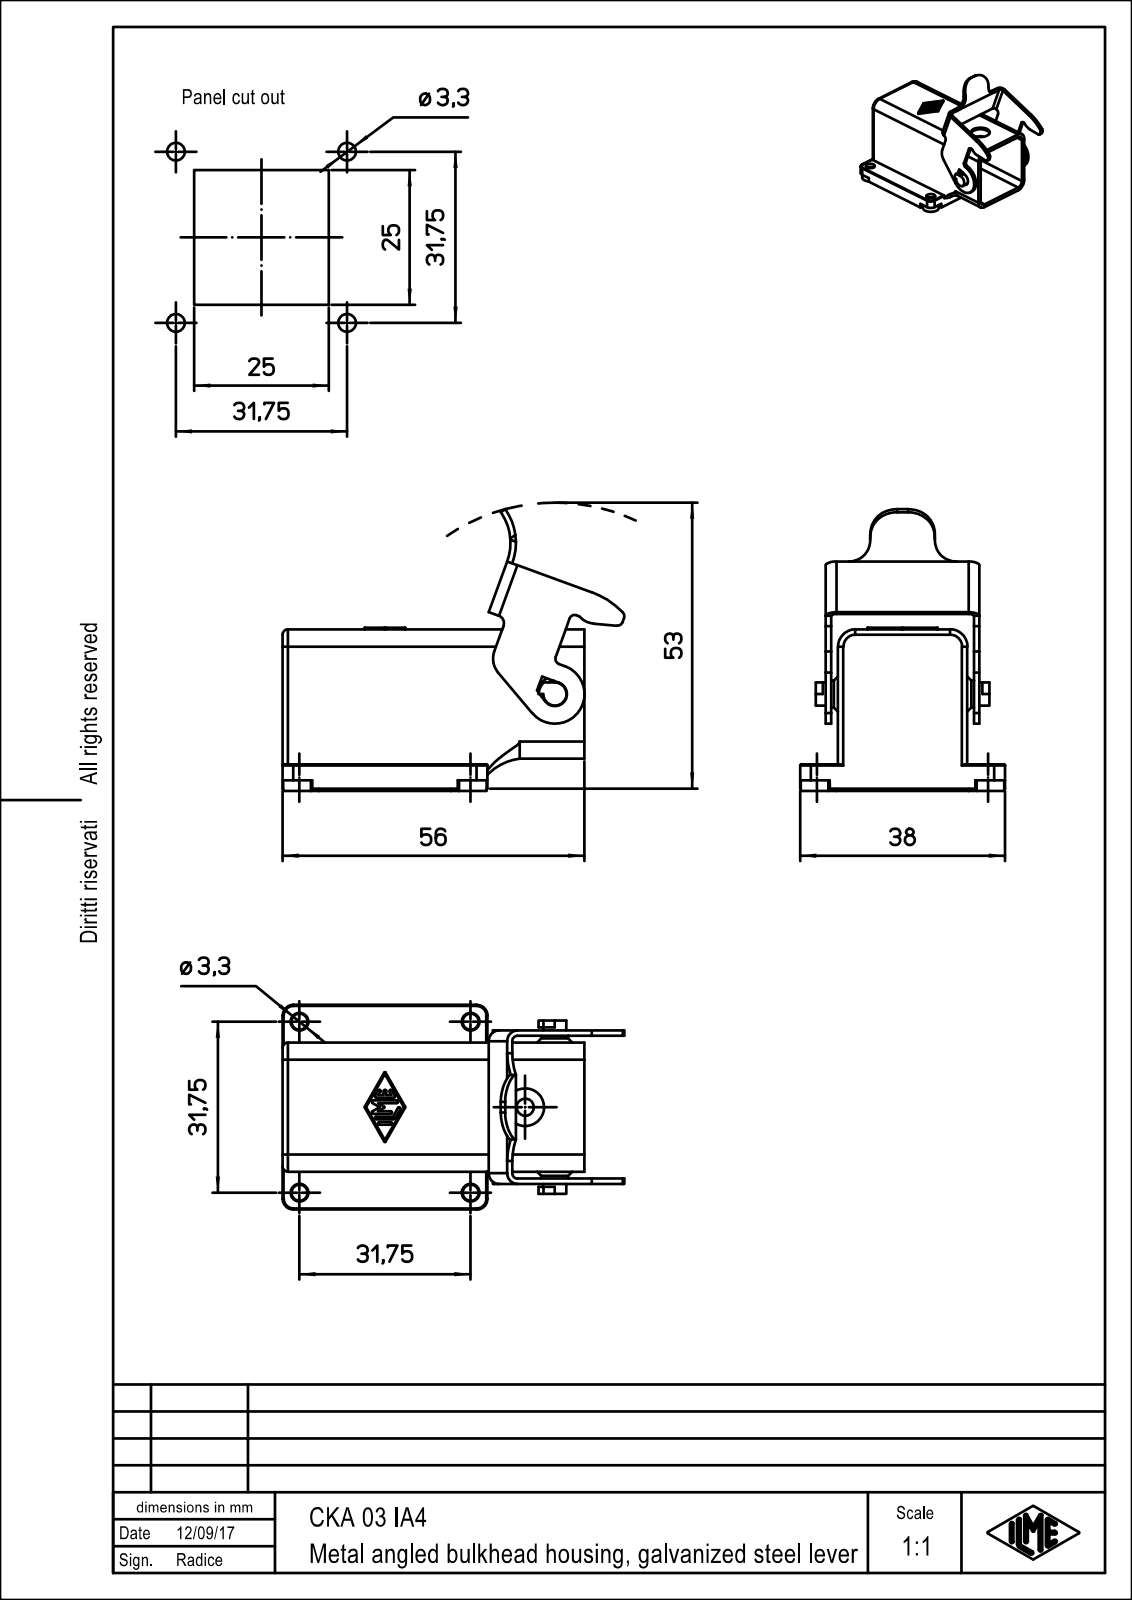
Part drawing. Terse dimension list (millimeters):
name: CKA_03_IA4
written by: PTC Creo Elements/Direct Modeling 19.0E 27-Jun-2016 (C) Parametric Technology GmbH (AUTOMOTIVE_DESIGN)
unit: mm
bodies: 1 solid, 310 faces (159 planar, 127 cylindrical, 24 other)
size: 63.4 × 52.31 × 38
volume: 14 191 mm³; area: 15 190 mm²
holes: 4× ⌀3, 4× ⌀3.3, 1× ⌀3.2, 1× ⌀7
bosses: 1× ⌀5, 1× ⌀4.3
rounds: 21× R2, 15× R0.25, 12× R3.2, 9× R1, 5× R3, 4× R0.2, 4× R0.5, 4× R4
face distances: 1.2, 22.8, 24, 25.05, 21.6, 1, 2.25, 27.5, 3.45, 26.25
hole spacings: 31.76, 18.84, 31.75, 44.79, 44.91, 31.74, 44.78, 44.9
